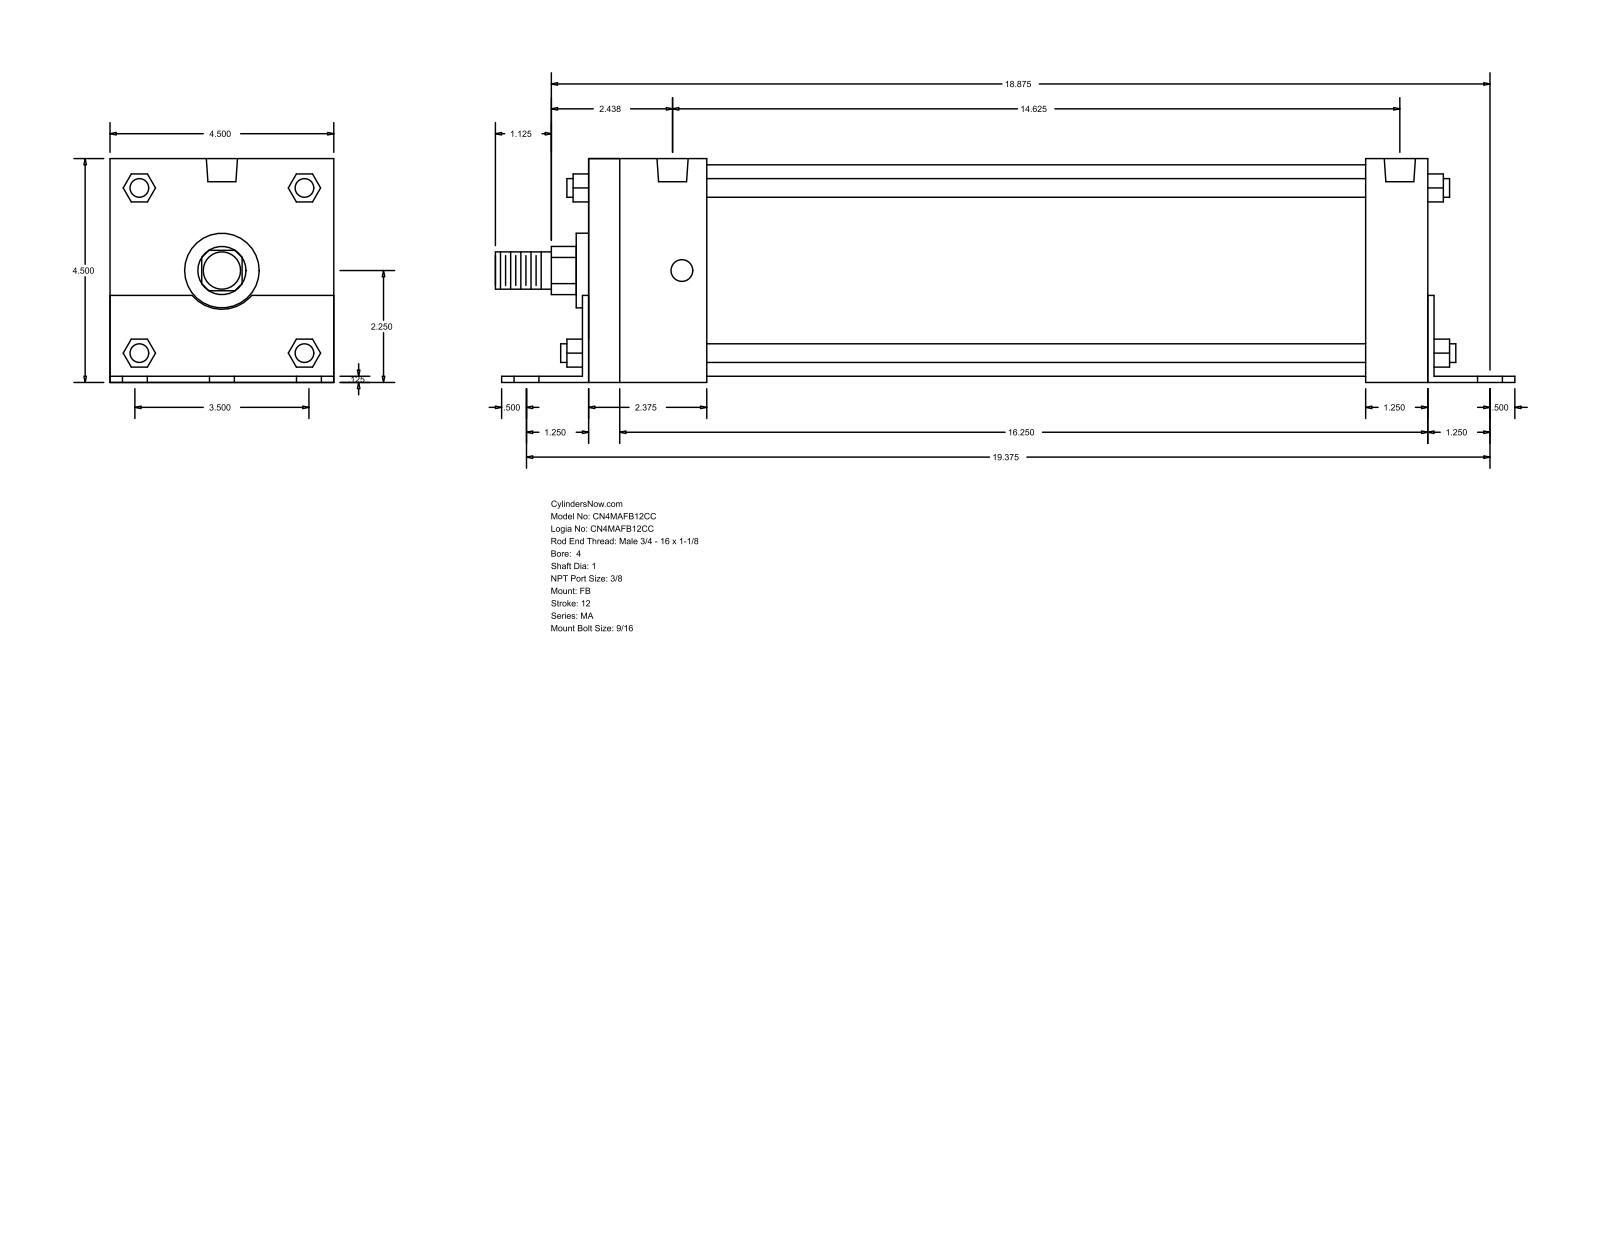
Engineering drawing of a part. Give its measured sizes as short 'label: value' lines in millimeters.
name: MA_FB__0400_1
written by: GSSL Pune (CONFIG_CONTROL_DESIGN)
unit: mm
bodies: 0 solids, 140 faces (105 planar, 35 cylindrical, 0 other)
size: 520.7 × 114.35 × 114.3
holes: 6× ⌀14.29, 4× ⌀11.11, 2× ⌀15.93
bosses: 4× ⌀9.53, 1× ⌀107.95, 1× ⌀38.1, 1× ⌀25.4, 1× ⌀19.05
rounds: 1× R12.29, 1× R19.81
face distances: 114.3, 3.17, 114.35, 431.8, 3.12, 111.18, 428.63, 434.97, 400.05, 396.88
hole spacings: 44.45, 494.13, 492.13, 64, 67.51, 86.85, 88.9, 90.97
